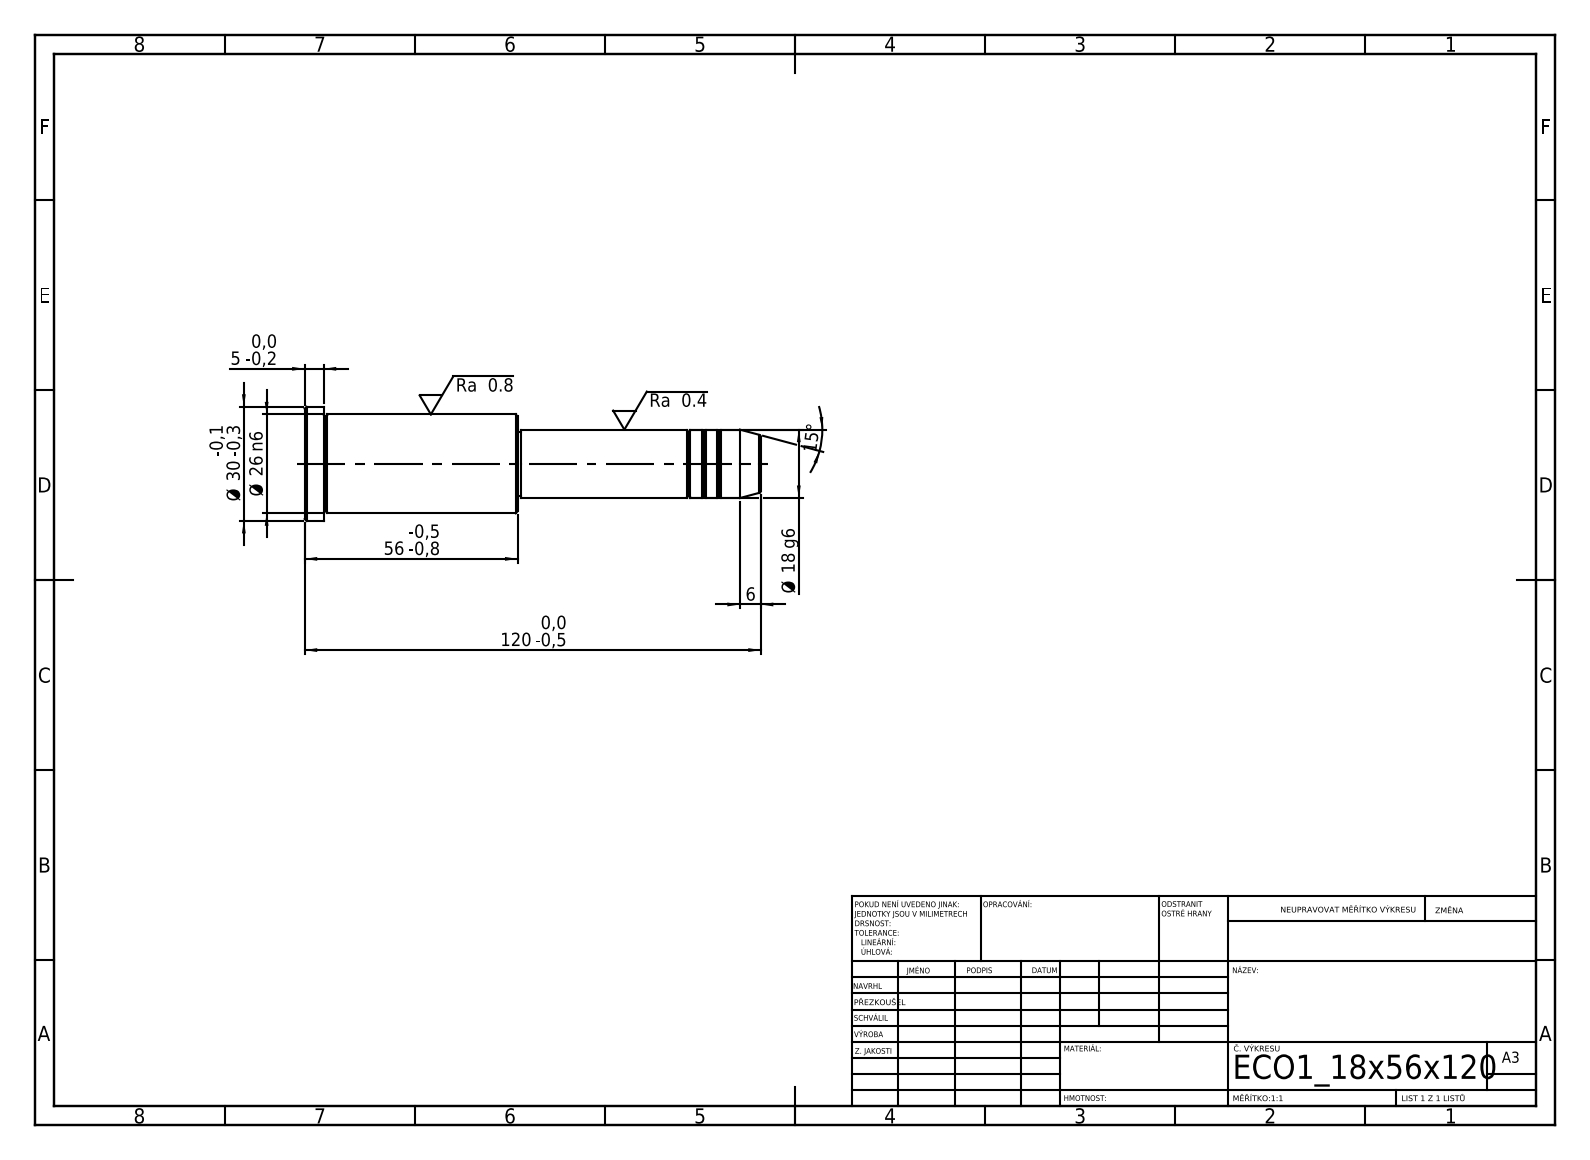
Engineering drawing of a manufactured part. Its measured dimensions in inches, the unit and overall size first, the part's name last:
Units: inches
Overall size (bounding box): 4.724 × 1.181 × 1.181
Round bosses / shafts (diameter × count): ⌀1.181 ×1, ⌀1.024 ×1, ⌀0.709 ×1, ⌀0.669 ×1
Main face-to-face distances: 2.205, 2.008, 0.197, 2.52, 4.528, 4.724, 2.48, 0.039, 2.047, 2.244
Volume: 2.84 in³ · Surface area: 15.04 in²
Bodies: 1 solid, 43 faces (5 planar, 14 cylindrical, 24 other)
STEP written by: SolidWorks 2019 (CONFIG_CONTROL_DESIGN)
